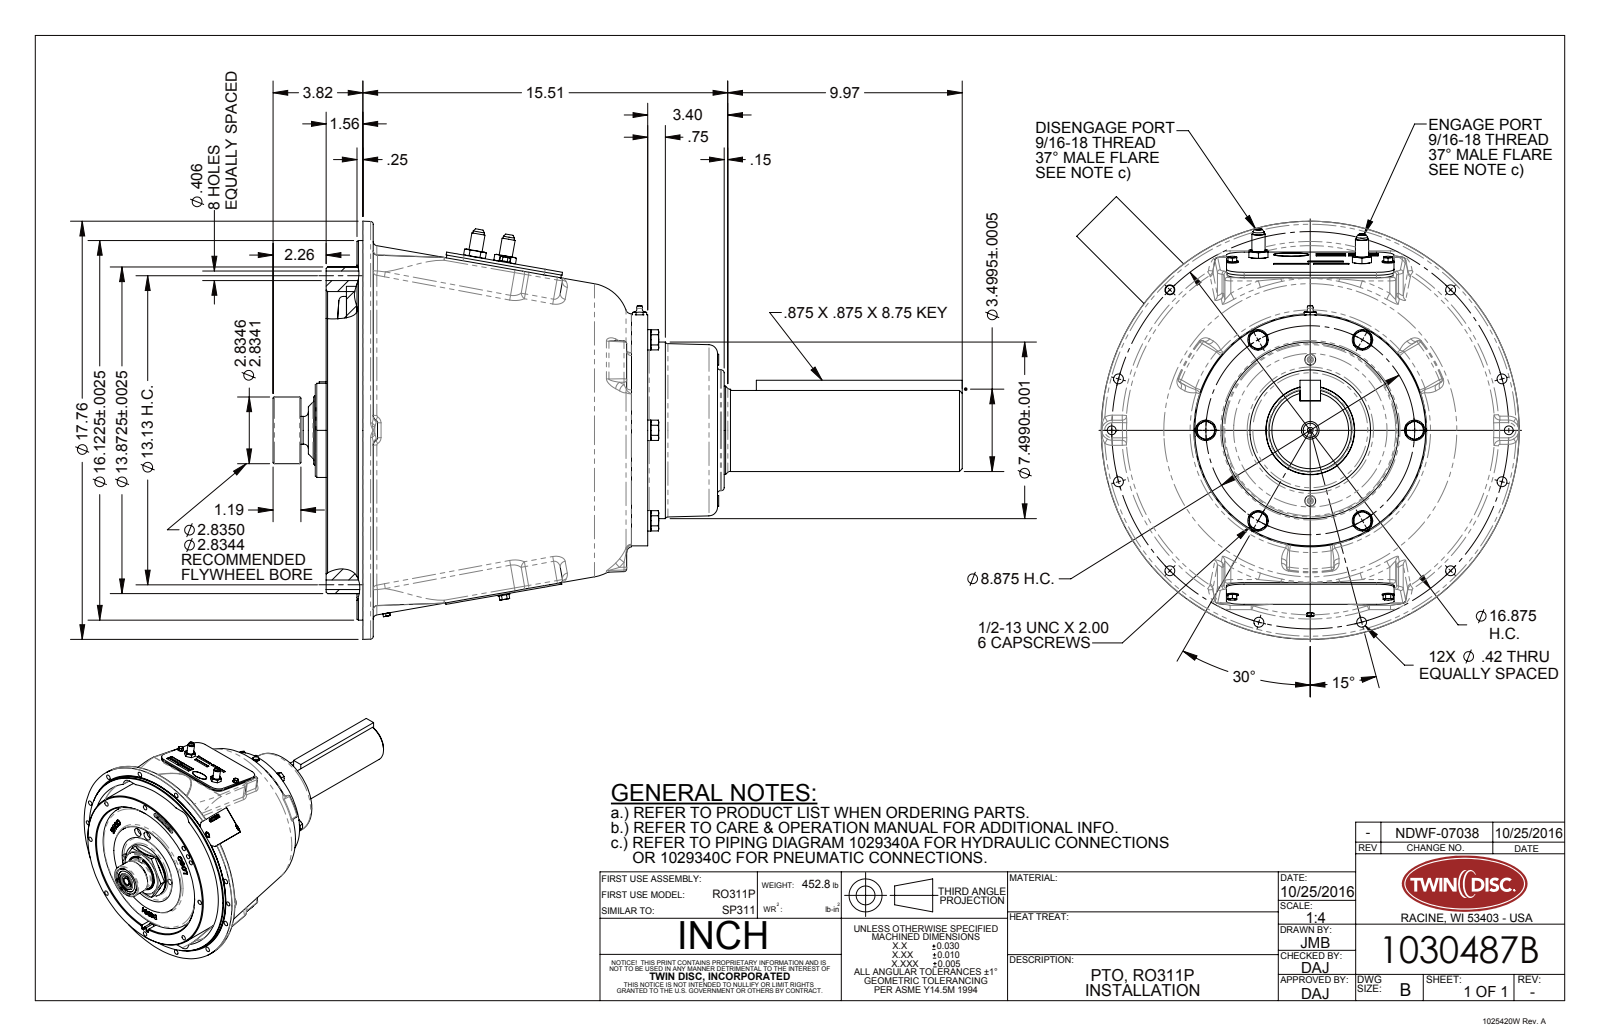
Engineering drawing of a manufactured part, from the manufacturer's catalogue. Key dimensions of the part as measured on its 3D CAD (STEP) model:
Part name (STEP PRODUCT): 1030487B
STEP written by: SolidWorks 2015 (AUTOMOTIVE_DESIGN)
Units: millimetres
Bodies: 0 solids, 1008 faces (320 planar, 224 cylindrical, 464 other)
Overall size (bounding box): 744.05 × 477.68 × 477.68
Round holes (diameter × count): ⌀10.72 ×12, ⌀10.32 ×8, ⌀9.53 ×4, ⌀7.54 ×2, ⌀12.7 ×2, ⌀19.05 ×2, ⌀7.94 ×1, ⌀9.52 ×1, ⌀29.99 ×1, ⌀49.18 ×1, ⌀61.68 ×1, ⌀95.89 ×1
Round bosses / shafts (diameter × count): ⌀22.07 ×6, ⌀12.7 ×5, ⌀18.87 ×4, ⌀14.29 ×2, ⌀12.22 ×2, ⌀11.68 ×2, ⌀409.51 ×1, ⌀352.36 ×1
Partial cylindrical surfaces — rounded edges, fillets, slot ends (radius × count): R3.05 ×17, R6.35 ×10, R19.05 ×8, R4.57 ×4, R15.75 ×4, R18.29 ×4, R52.12 ×4, R1.21 ×2
Main face-to-face distances: 21.67, 3.18, 1.63, 39.62, 17.95, 11.18, 32.85, 50.8, 48.46, 37.28
Hole centre spacings: 214.31, 414.02, 68.58, 108.81, 127.57, 303.08, 307.99, 368.22
